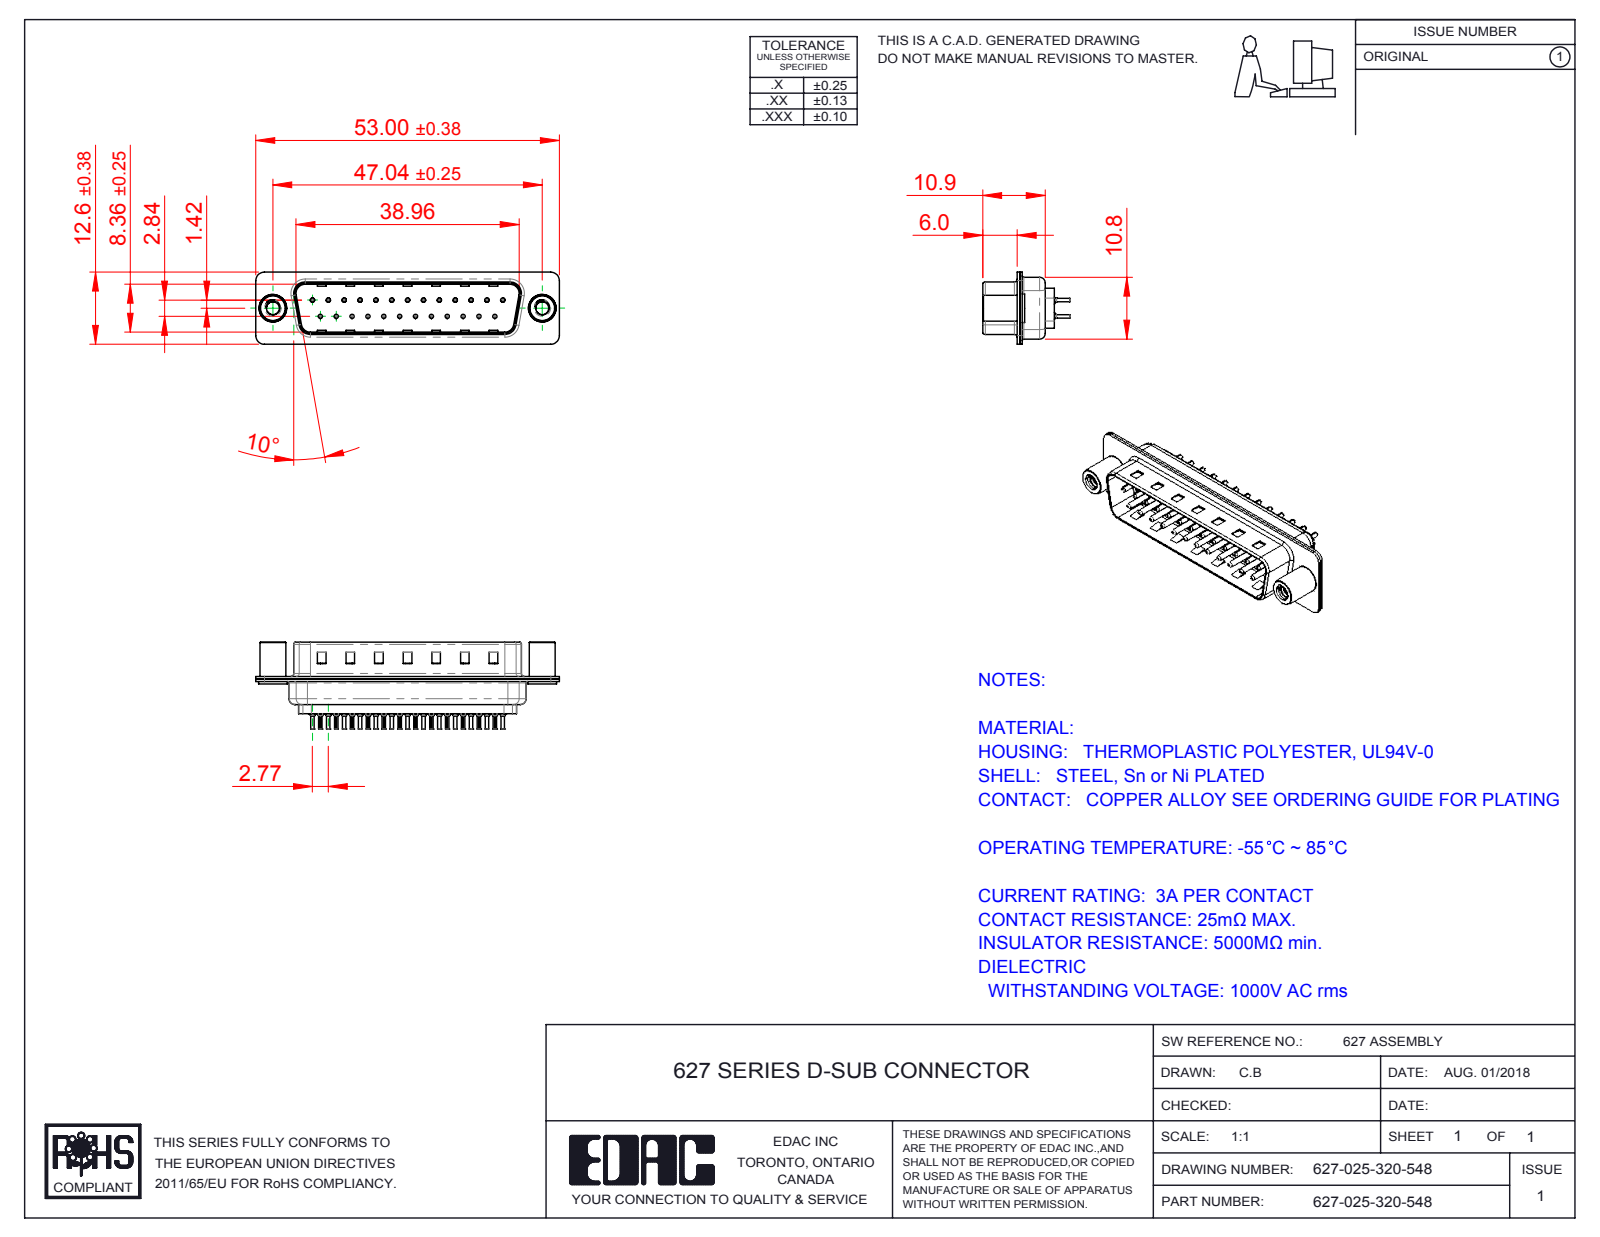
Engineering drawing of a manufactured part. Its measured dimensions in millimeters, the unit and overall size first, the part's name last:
Units: millimetres
Overall size (bounding box): 53 × 15.2 × 12.6
Round holes (diameter × count): ⌀0.2 ×25, ⌀0.35 ×25, ⌀1.1 ×25, ⌀1.6 ×25, ⌀2.26 ×2, ⌀4 ×2, ⌀4.8 ×2
Round bosses / shafts (diameter × count): ⌀2 ×25, ⌀1.5 ×25, ⌀0.75 ×25, ⌀0.6 ×25, ⌀5 ×2, ⌀4.9 ×2, ⌀4.5 ×2
Partial cylindrical surfaces — rounded edges, fillets, slot ends (radius × count): R0.1 ×50, R1.5 ×16, R2 ×12, R0.5 ×8, R1.6 ×8, R0.25 ×4, R0.6 ×4, R0.65 ×4
Main face-to-face distances: 0.4, 0.45, 0.82, 9.58, 0.9, 8.76, 1.5, 1.4, 6.5, 6.05
Hole centre spacings: 3.16, 8.31, 2.77, 5.54, 11.08, 16.62, 5.03, 5.04
Volume: 2 733 mm³ · Surface area: 7 853 mm²
Bodies: 30 solids, 2860 faces (773 planar, 1090 cylindrical, 997 other)
Part name (STEP PRODUCT): 627 Shell Rear_25 Contacts; 627-025-320-548; 627 Contact Row 2_20L; 627 Contact Row 1_20L (+3 more)
STEP written by: SolidWorks 2016 (CONFIG_CONTROL_DESIGN)
